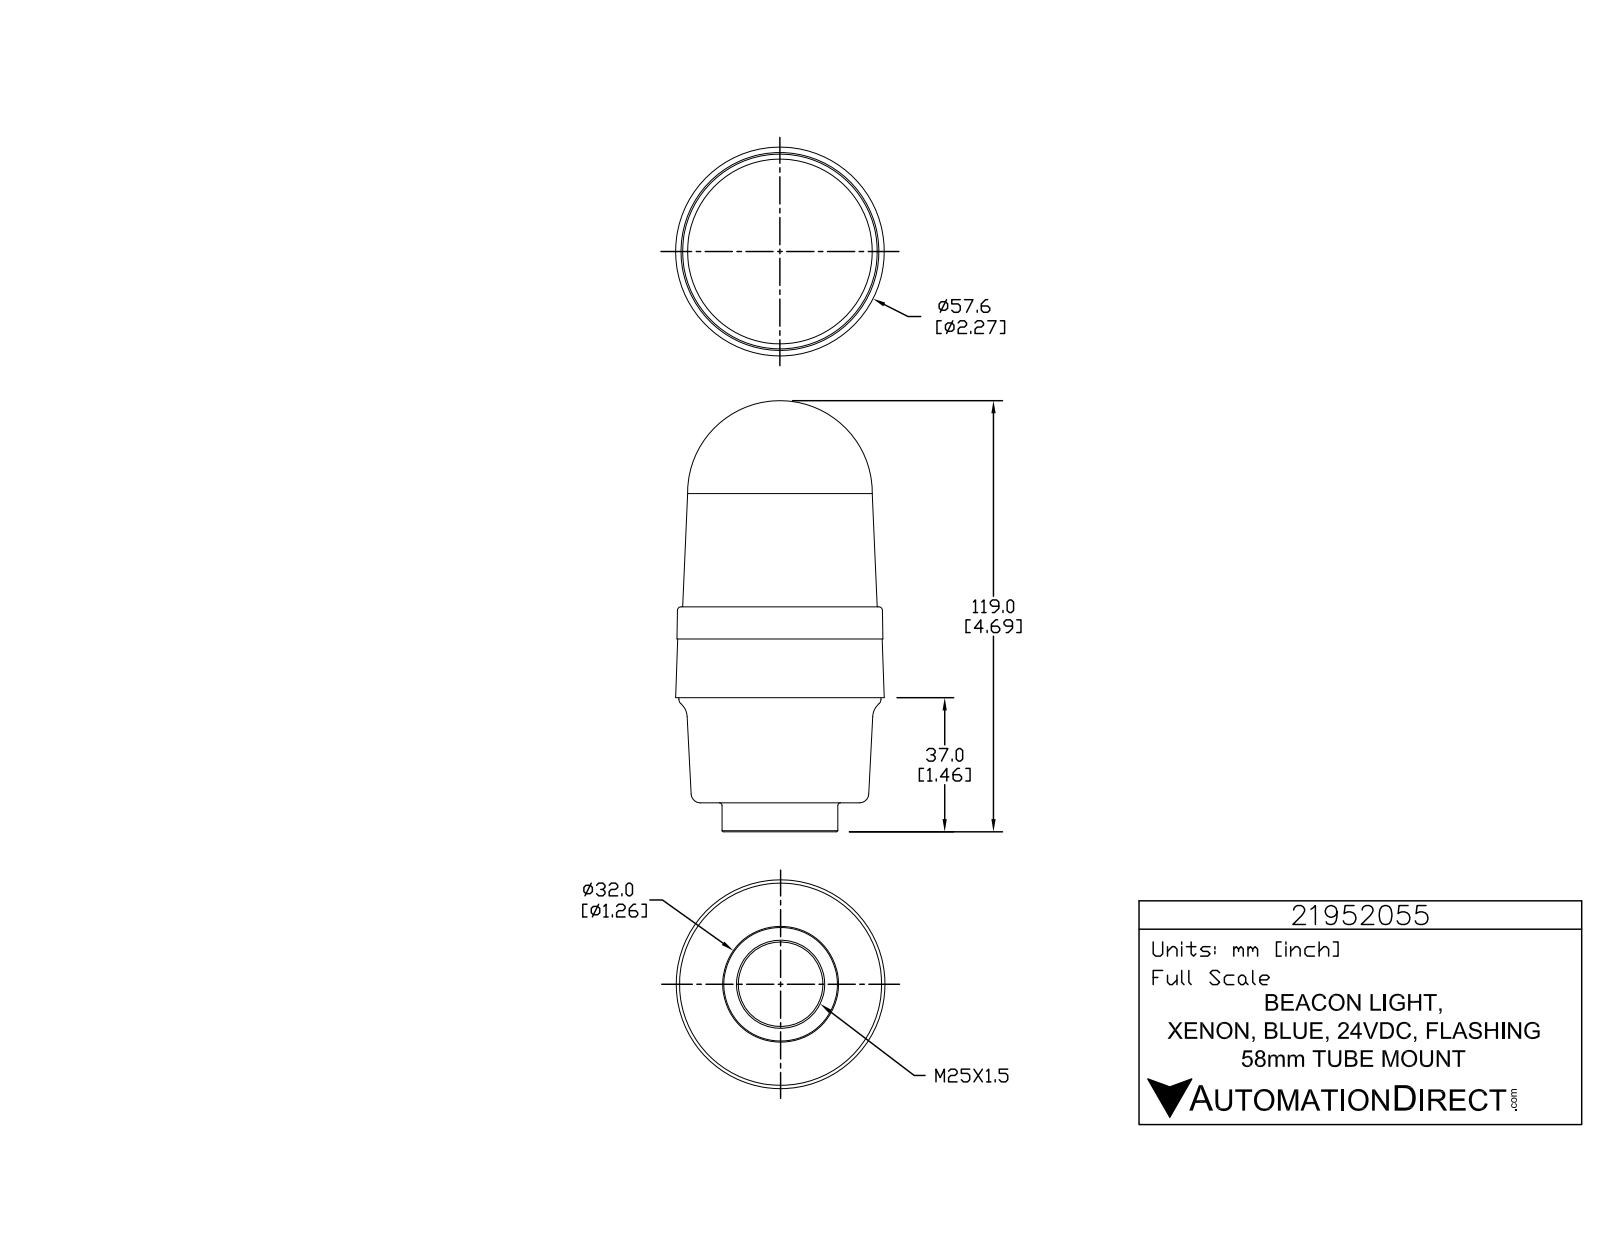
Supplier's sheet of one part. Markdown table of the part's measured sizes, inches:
| quantity | value |
| --- | --- |
| part name | 21952055 |
| STEP written by | SolidWorks 2015 (AUTOMOTIVE_DESIGN) |
| units | inches |
| bodies | 1 solid, 791 faces (525 planar, 168 cylindrical, 98 other) |
| overall size | 4.685 × 2.269 × 2.269 |
| volume | 13.89 in³ |
| surface area | 34.06 in² |
| round holes (diameter × count) | 0.039 × 3, 0.92 × 1 |
| round bosses / shafts (diameter × count) | 0.226 × 3, 0.056 × 3, 2.197 × 1, 1.26 × 1 |
| partial cylindrical surfaces (radius × count) | 0.008 × 6, 0.008 × 6, 0.008 × 6, 0.131 × 6, 0.004 × 3, 0.005 × 3, 0.008 × 3, 0.008 × 3 |
| main face-to-face distances | 0.315, 1.142, 1.457, 0.988, 2.13, 2.445, 0.35, 0.638, 1.78, 2.094 |
